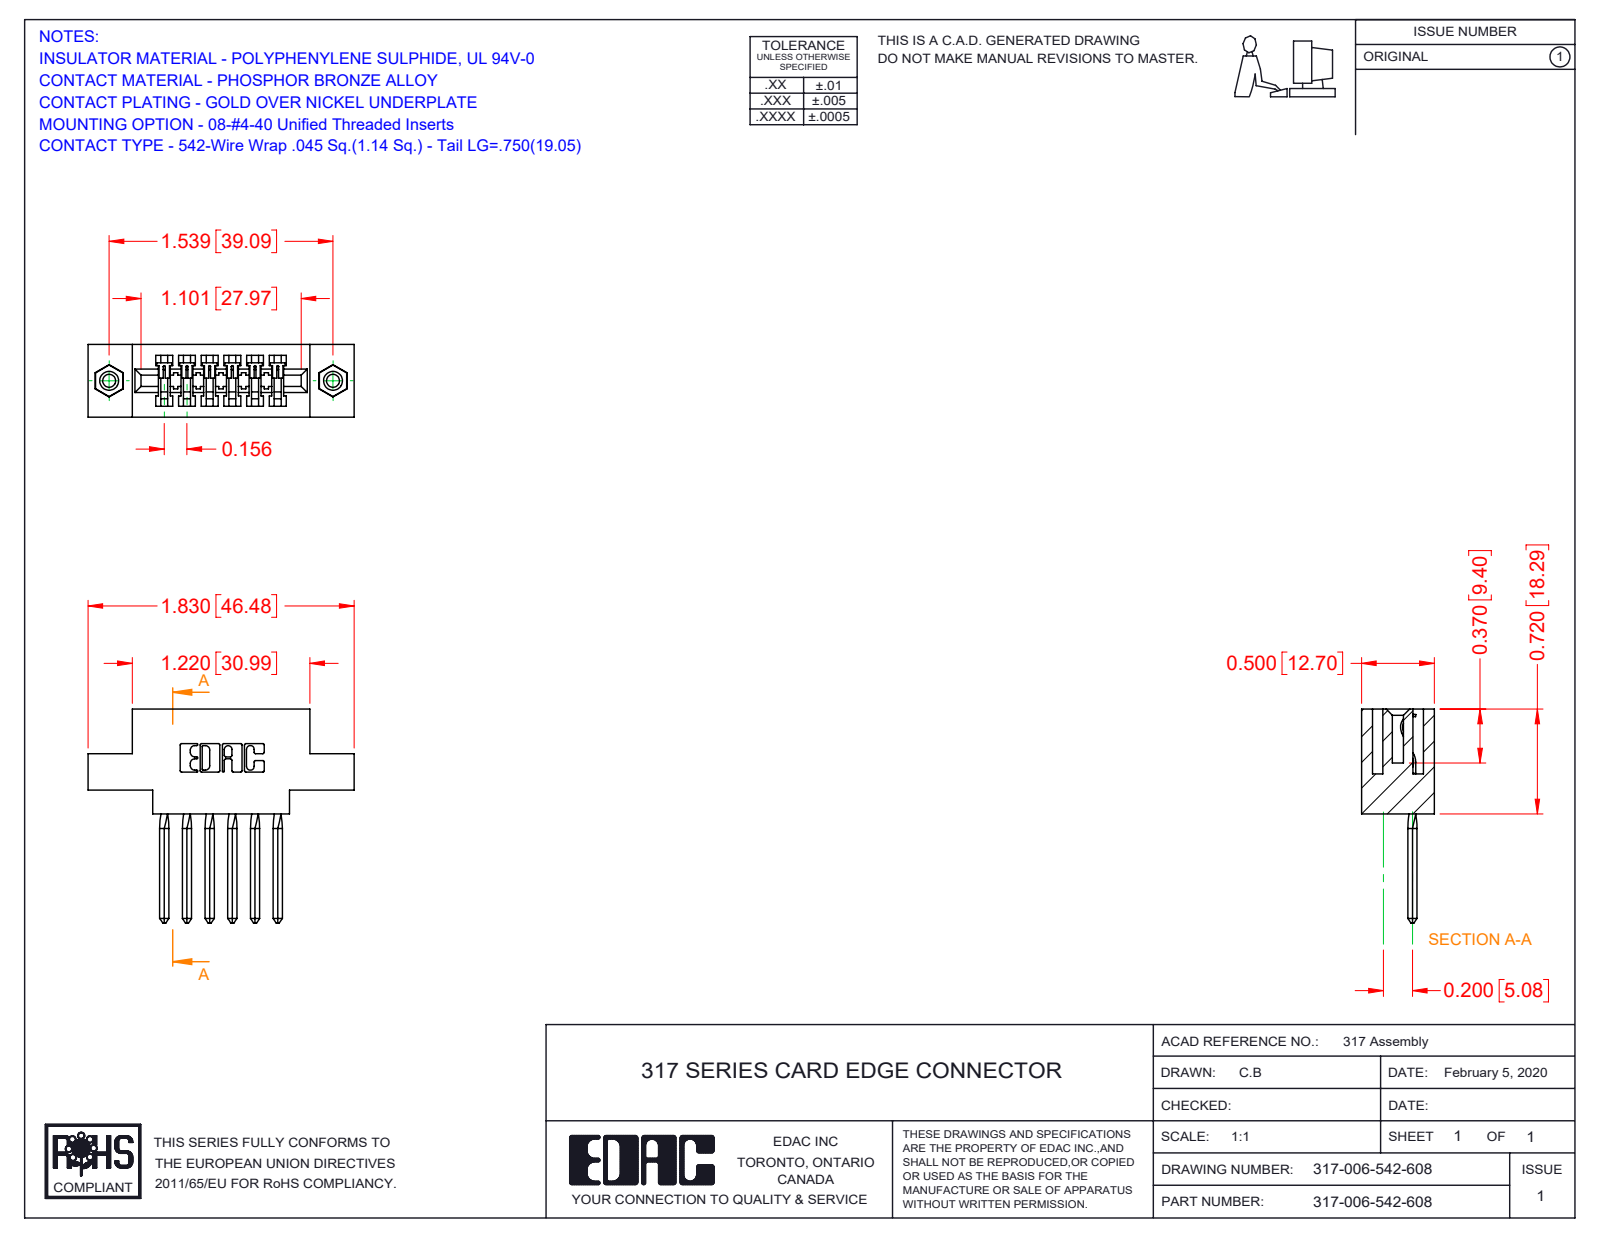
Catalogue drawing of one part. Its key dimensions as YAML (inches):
part_name: "317-006-542-678; 317 Part_.156 Dia - TI; 317-290-003_542; 345-250-001_345-250-003-102"
step_written_by: "SolidWorks 2016 (CONFIG_CONTROL_DESIGN)"
units: inches
bodies: {solids: 9, faces: 612, planar: 474, cylindrical: 98, other: 40}
overall_size: [1.83, 1.47, 0.5]
volume: 0.379
surface_area: 10.54
round_holes:
  - {diameter: 0.089, count: 2}
  - {diameter: 0.125, count: 2}
  - {diameter: 0.156, count: 2}
round_bosses_or_shafts:
  - {diameter: 0.155, count: 2}
partial_cylinders:
  - {radius: 0.01, count: 22}
  - {radius: 0.006, count: 12}
  - {radius: 0.007, count: 6}
  - {radius: 0.031, count: 6}
  - {radius: 0.026, count: 3}
  - {radius: 0.074, count: 1}
  - {radius: 0.089, count: 1}
  - {radius: 0.1, count: 1}
face_to_face_distances: [0.5, 0.075, 0.425, 0.156, 0.11, 0.065, 0.116, 0.163, 0.136, 0.305]
hole_center_spacings: [1.539]
